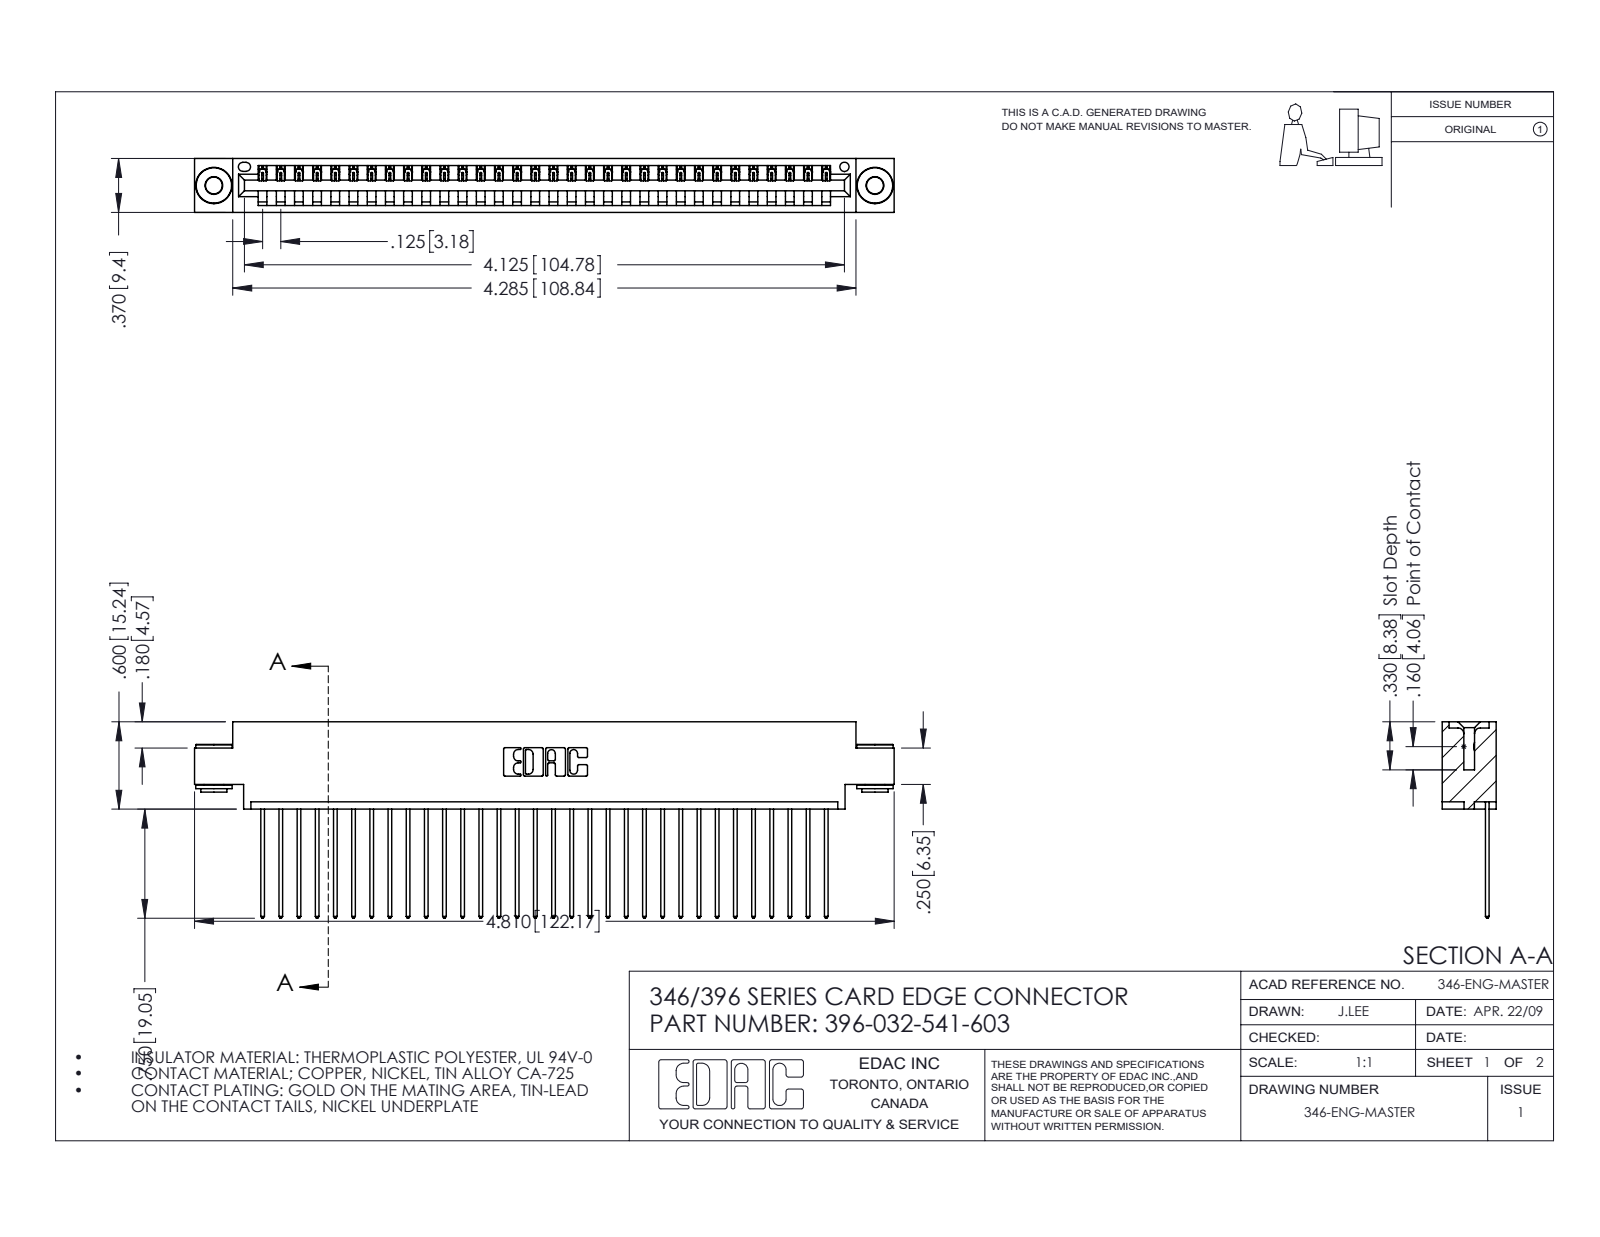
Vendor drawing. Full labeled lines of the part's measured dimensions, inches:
Part name (STEP PRODUCT): 396-032-541-603; 346 Part_0.170 Offset - 0.156 Dia-TH; 345-292-001_345-293-141; 345-250-002_345-250-002-102
STEP written by: SolidWorks 2016 (CONFIG_CONTROL_DESIGN)
Units: inches
Bodies: 35 solids, 2020 faces (1370 planar, 642 cylindrical, 8 other)
Overall size (bounding box): 4.81 × 1.35 × 0.37
Volume: 0.708 in³ · Surface area: 23.86 in²
Round holes (diameter × count): ⌀0.116 ×2, ⌀0.156 ×2, ⌀0.064 ×1
Round bosses / shafts (diameter × count): ⌀0.25 ×2, ⌀0.18 ×2, ⌀0.136 ×2
Partial cylindrical surfaces — rounded edges, fillets, slot ends (radius × count): R0.006 ×64, R0.01 ×64, R0.01 ×22, R0.007 ×6, R0.031 ×6, R0.026 ×3, R0.031 ×2, R0.04 ×2
Main face-to-face distances: 0.048, 0.322, 0.37, 0.25, 0.025, 0.072, 0.298, 0.148, 0.222, 0.1
Hole centre spacings: 0.246, 4.337, 4.545
